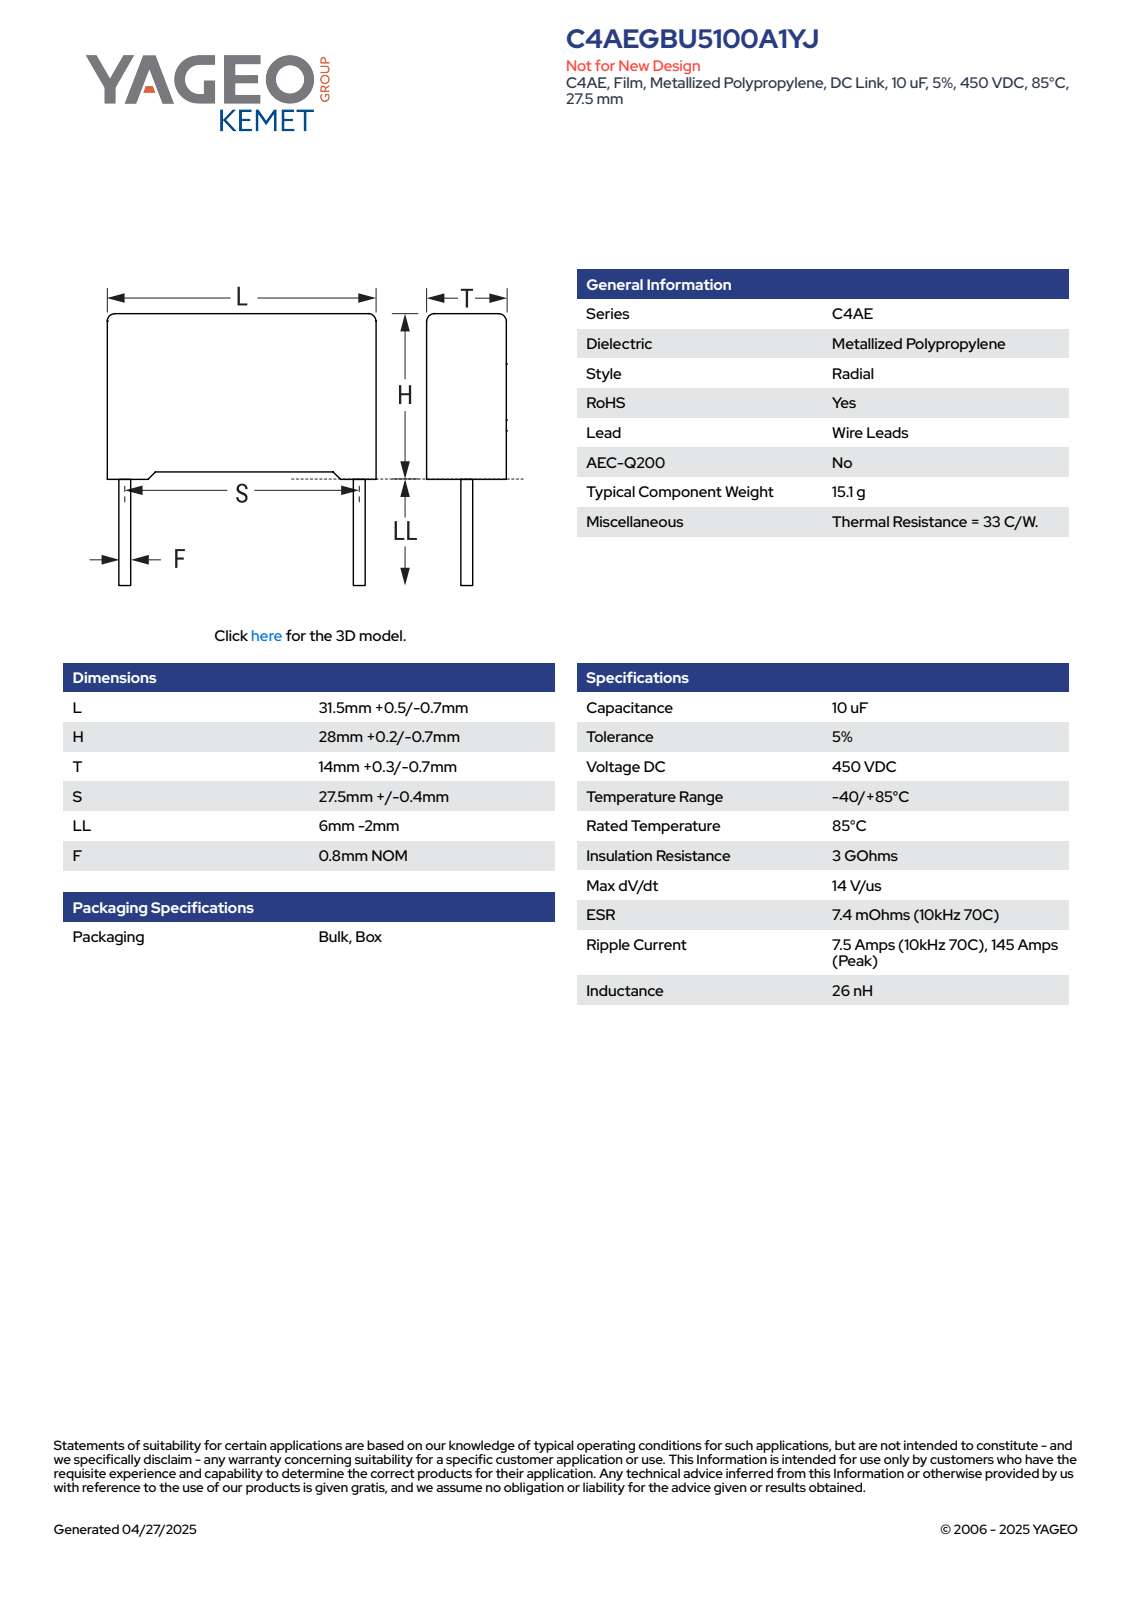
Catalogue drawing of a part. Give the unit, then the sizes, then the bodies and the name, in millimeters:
Units: millimetres
Overall size (bounding box): 32.2 × 32 × 14.3
Round bosses / shafts (diameter × count): ⌀0.8 ×2
Partial cylindrical surfaces — rounded edges, fillets, slot ends (radius × count): R0.5 ×4
Main face-to-face distances: 14.3, 32, 27.23, 27.45, 0.75, 0.97, 28.2, 1.07, 30.93, 29.86
Volume: 12 521 mm³ · Surface area: 3 593 mm²
Bodies: 4 solids, 85 faces (77 planar, 8 cylindrical, 0 other)
Part name (STEP PRODUCT): CFR_RB2CFP_31.5X28X14_L32H28.2T14.3S27.5LL4F0.8
STEP written by: SolidWorks 2014 (AUTOMOTIVE_DESIGN)
